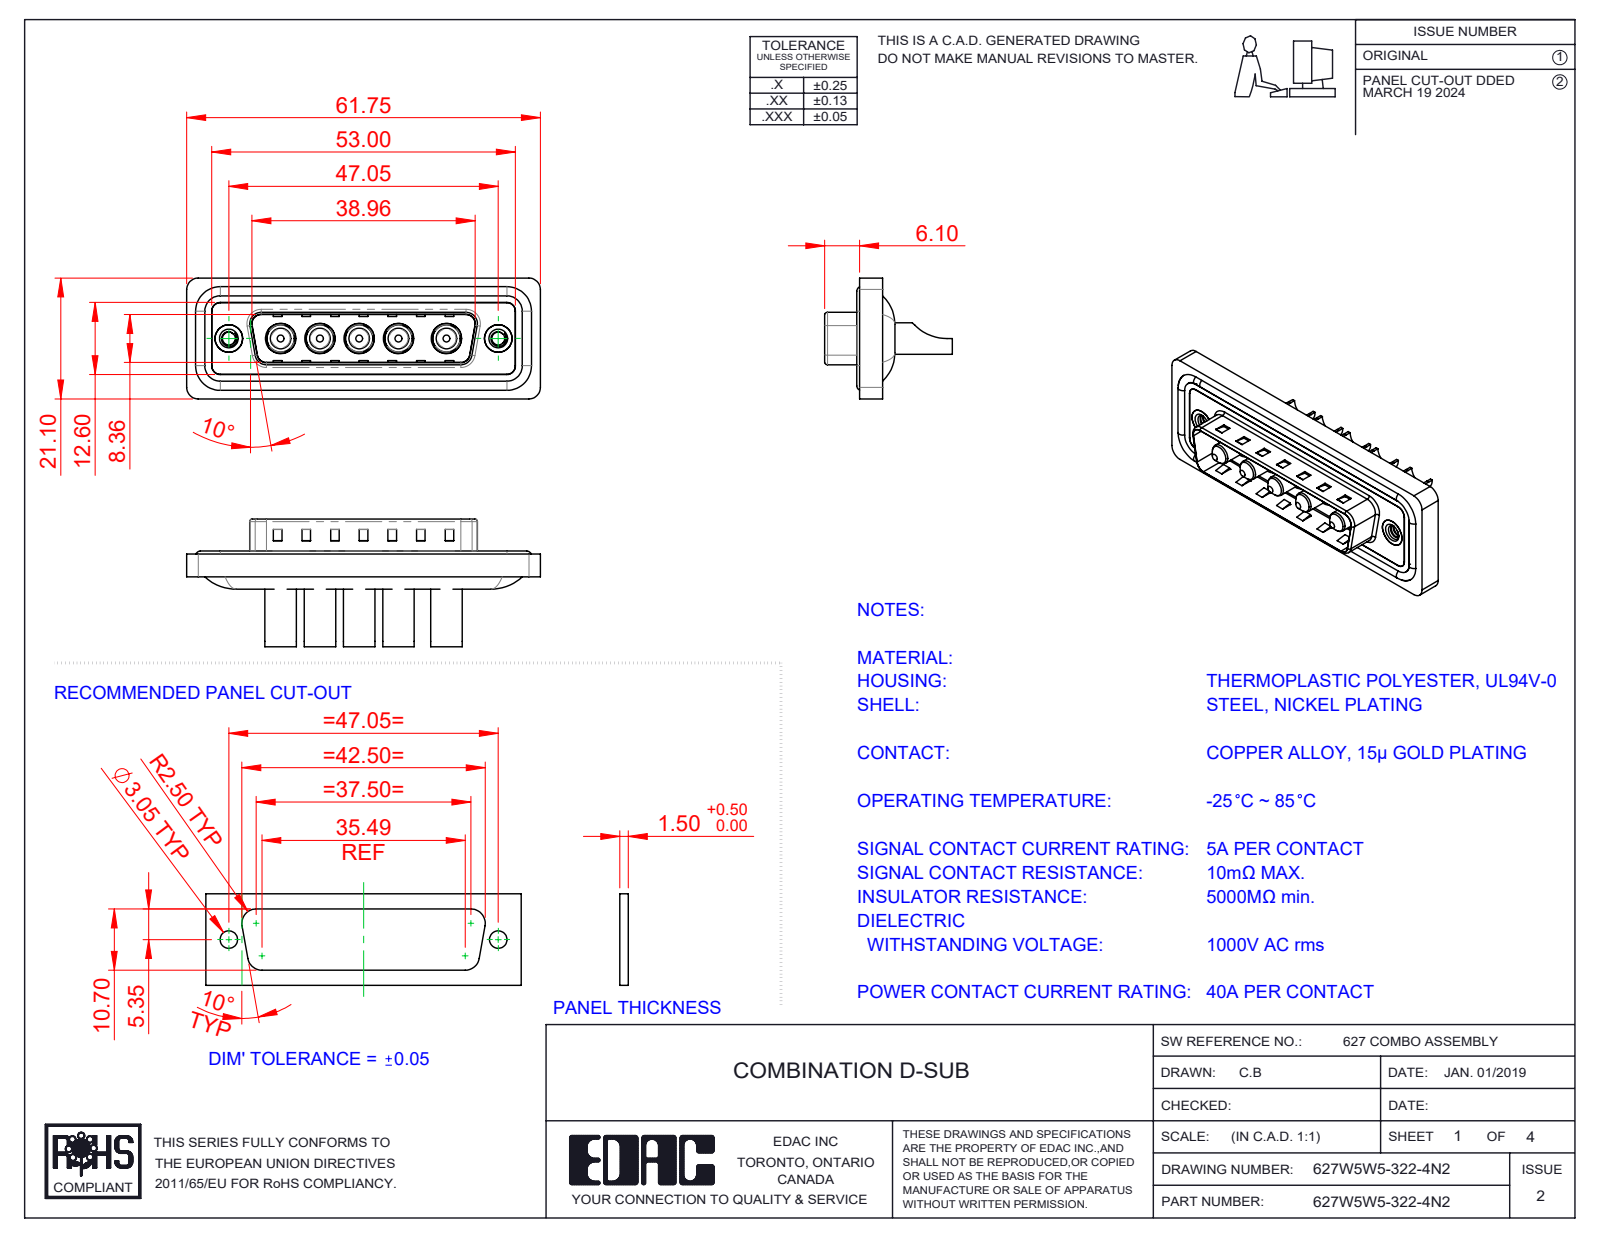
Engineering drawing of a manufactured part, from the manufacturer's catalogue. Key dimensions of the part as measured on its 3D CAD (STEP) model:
Part name (STEP PRODUCT): 627Combo Shell Rear_25 Contacts; 627Combo Waterproof Housing_25 Contacts; 627Combo Housing_5W5; 627W5W5-322-4N2 (+3 more)
STEP written by: SolidWorks 2023 (CONFIG_CONTROL_DESIGN)
Units: millimetres
Bodies: 17 solids, 698 faces (269 planar, 288 cylindrical, 141 other)
Overall size (bounding box): 61.75 × 22.3 × 21.1
Volume: 7 672 mm³ · Surface area: 12 496 mm²
Round holes (diameter × count): ⌀4.6 ×5, ⌀4.85 ×5, ⌀5.3 ×5, ⌀2.26 ×2, ⌀4 ×2, ⌀4.8 ×2, ⌀5 ×2
Round bosses / shafts (diameter × count): ⌀5.5 ×5, ⌀5.2 ×5, ⌀4.75 ×5, ⌀3.75 ×5, ⌀3.6 ×5, ⌀1.6 ×4, ⌀4.9 ×2
Partial cylindrical surfaces — rounded edges, fillets, slot ends (radius × count): R1.5 ×22, R2 ×18, R0.5 ×8, R1.6 ×8, R2.1 ×5, R0.25 ×4, R0.6 ×4, R0.65 ×4
Main face-to-face distances: 0.4, 0.5, 1.1, 1.5, 3.1, 1.6, 2.9, 0.82, 9.58, 5.65
Hole centre spacings: 6.86, 9.04, 13.73, 38.01, 6.87, 8.37, 8.38, 9.05
